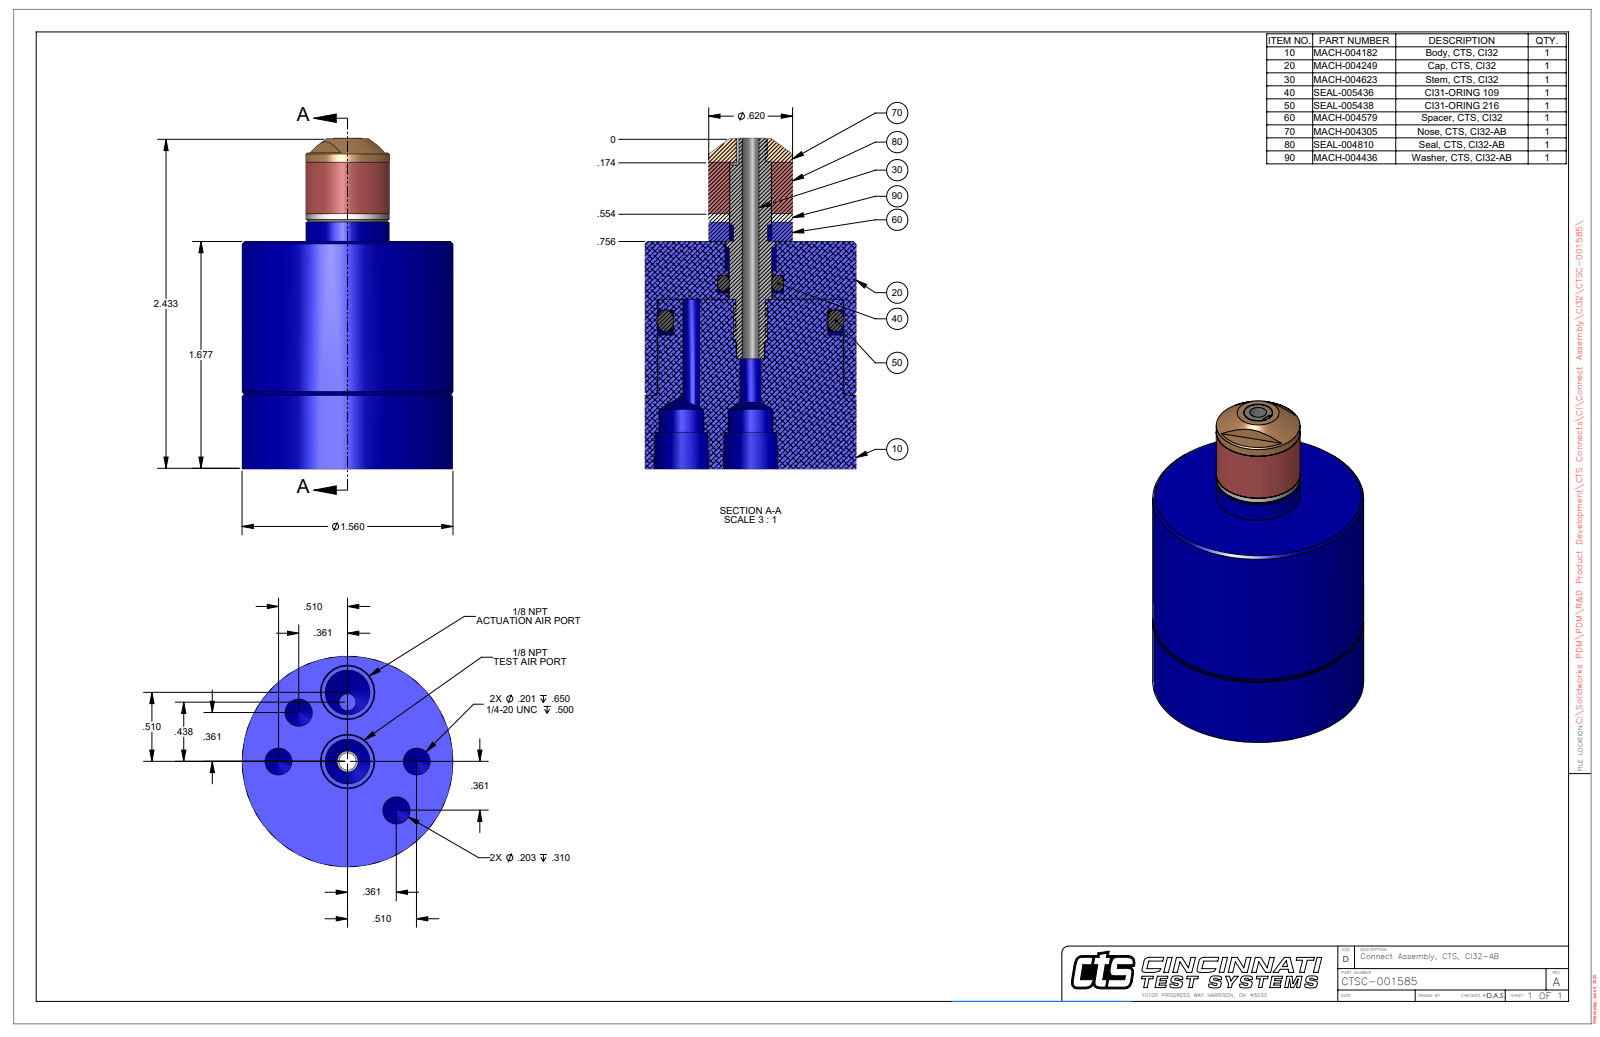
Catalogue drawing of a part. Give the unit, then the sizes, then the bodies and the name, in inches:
Units: inches
Overall size (bounding box): 2.437 × 1.56 × 1.56
Round holes (diameter × count): ⌀0.125 ×2, ⌀0.201 ×2, ⌀0.203 ×2, ⌀0.332 ×2, ⌀0.156 ×1, ⌀0.314 ×1, ⌀0.38 ×1, ⌀1.377 ×1
Round bosses / shafts (diameter × count): ⌀1.56 ×1, ⌀1.365 ×1, ⌀0.62 ×1, ⌀0.618 ×1, ⌀0.357 ×1, ⌀0.31 ×1
Partial cylindrical surfaces — rounded edges, fillets, slot ends (radius × count): R0.106 ×1
Main face-to-face distances: 1.677, 0.542, 1.135, 2.329, 1.787, 0.652, 0.273, 0.269, 1.404, 2.056
Hole centre spacings: 0.51, 0.39, 0.942, 0.672, 0.721, 0.072, 0.369, 0.437
Volume: 3.21 in³ · Surface area: 19.53 in²
Bodies: 1 solid, 102 faces (29 planar, 39 cylindrical, 34 other)
Part name (STEP PRODUCT): CTSC-001585
STEP written by: SolidWorks 2023 (AUTOMOTIVE_DESIGN)
